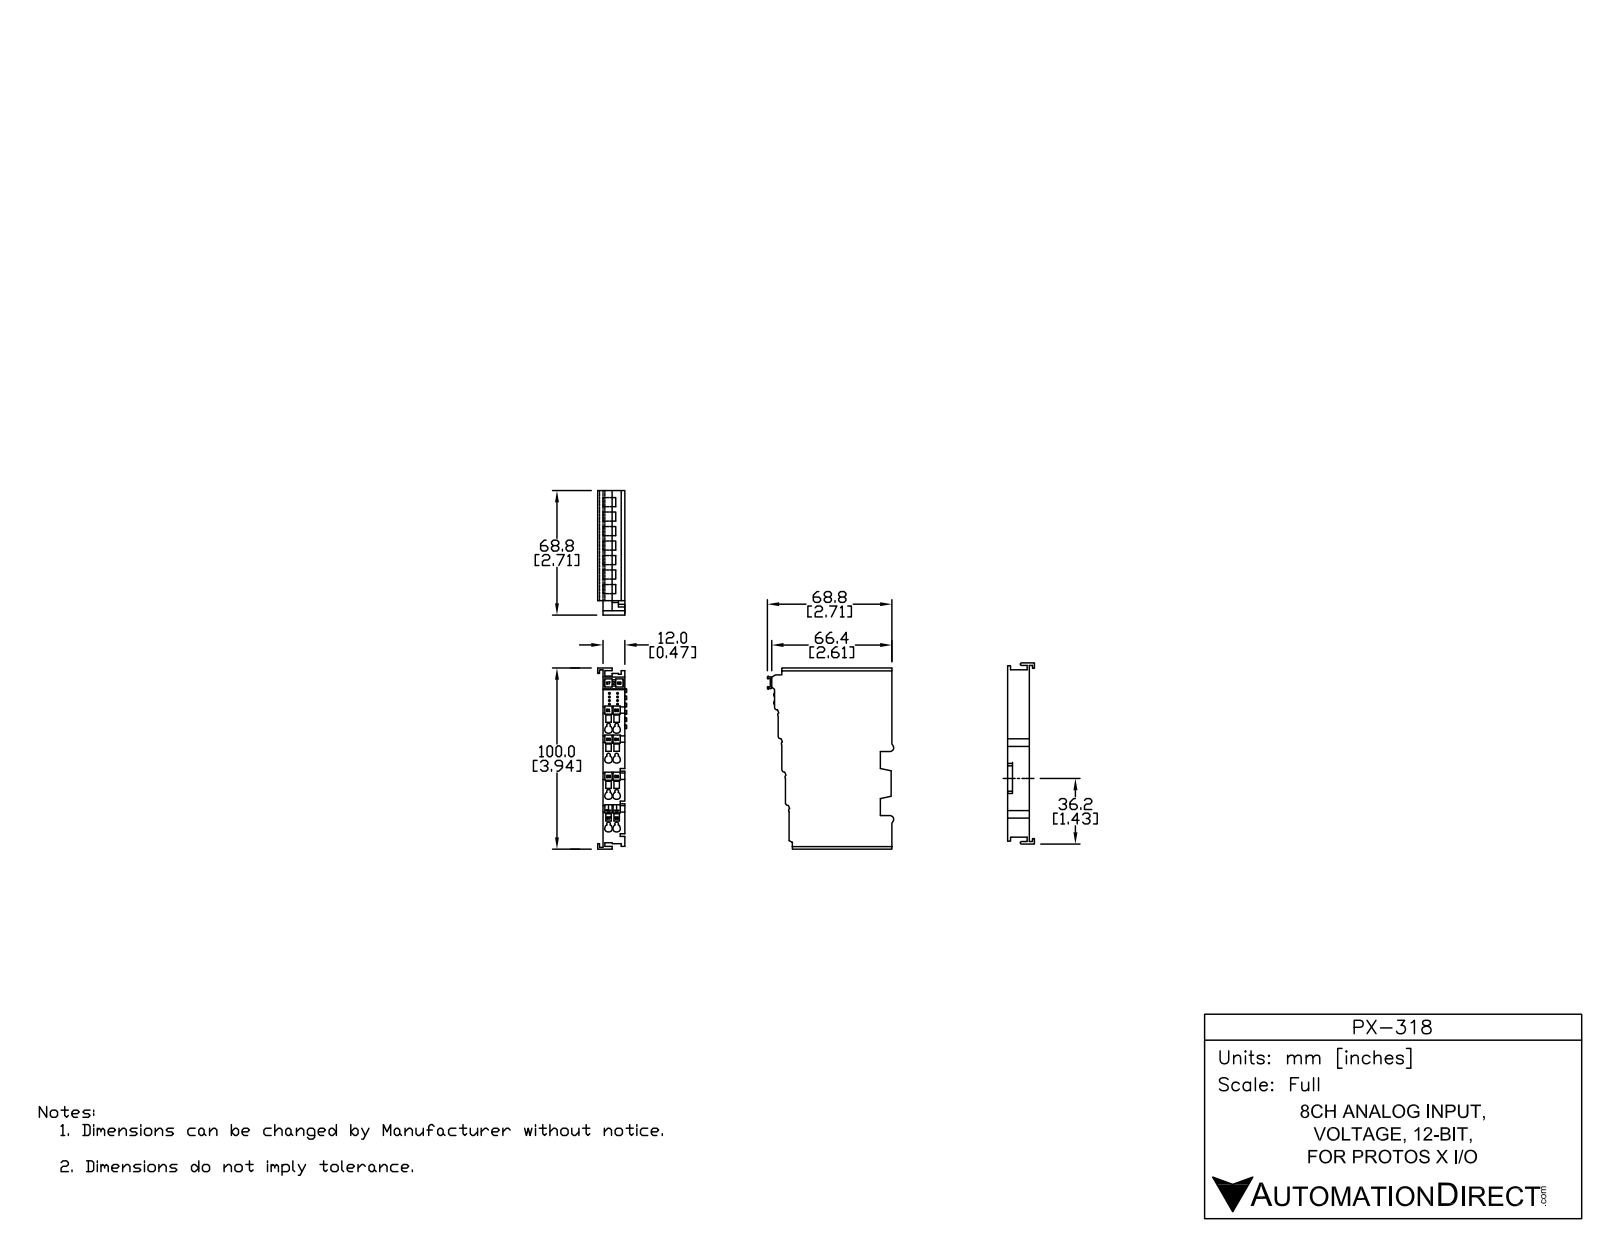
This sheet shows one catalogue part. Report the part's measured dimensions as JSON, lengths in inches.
{"part_name": "PX-318", "step_written_by": "SolidWorks 2014 (AUTOMOTIVE_DESIGN)", "units": "inches", "bodies": {"solids": 26, "faces": 1425, "planar": 1011, "cylindrical": 354, "other": 60}, "overall_size": [3.947, 2.728, 0.596], "volume_in3": 3.606, "surface_area_in2": 50.13, "round_holes": [[0.157, 8]], "partial_cylinders_radius": [[0.01, 67], [0.012, 43], [0.015, 12], [0.016, 10], [0.039, 8], [0.007, 4], [0.041, 4], [0.054, 4]], "face_to_face_distances": [0.472, 0.079, 0.394, 0.039, 0.073, 0.433, 0.157, 0.343, 0.124, 0.048], "hole_center_spacings": [0.197, 0.724, 0.751, 0.63, 0.66, 1.354, 1.369, 1.449]}
